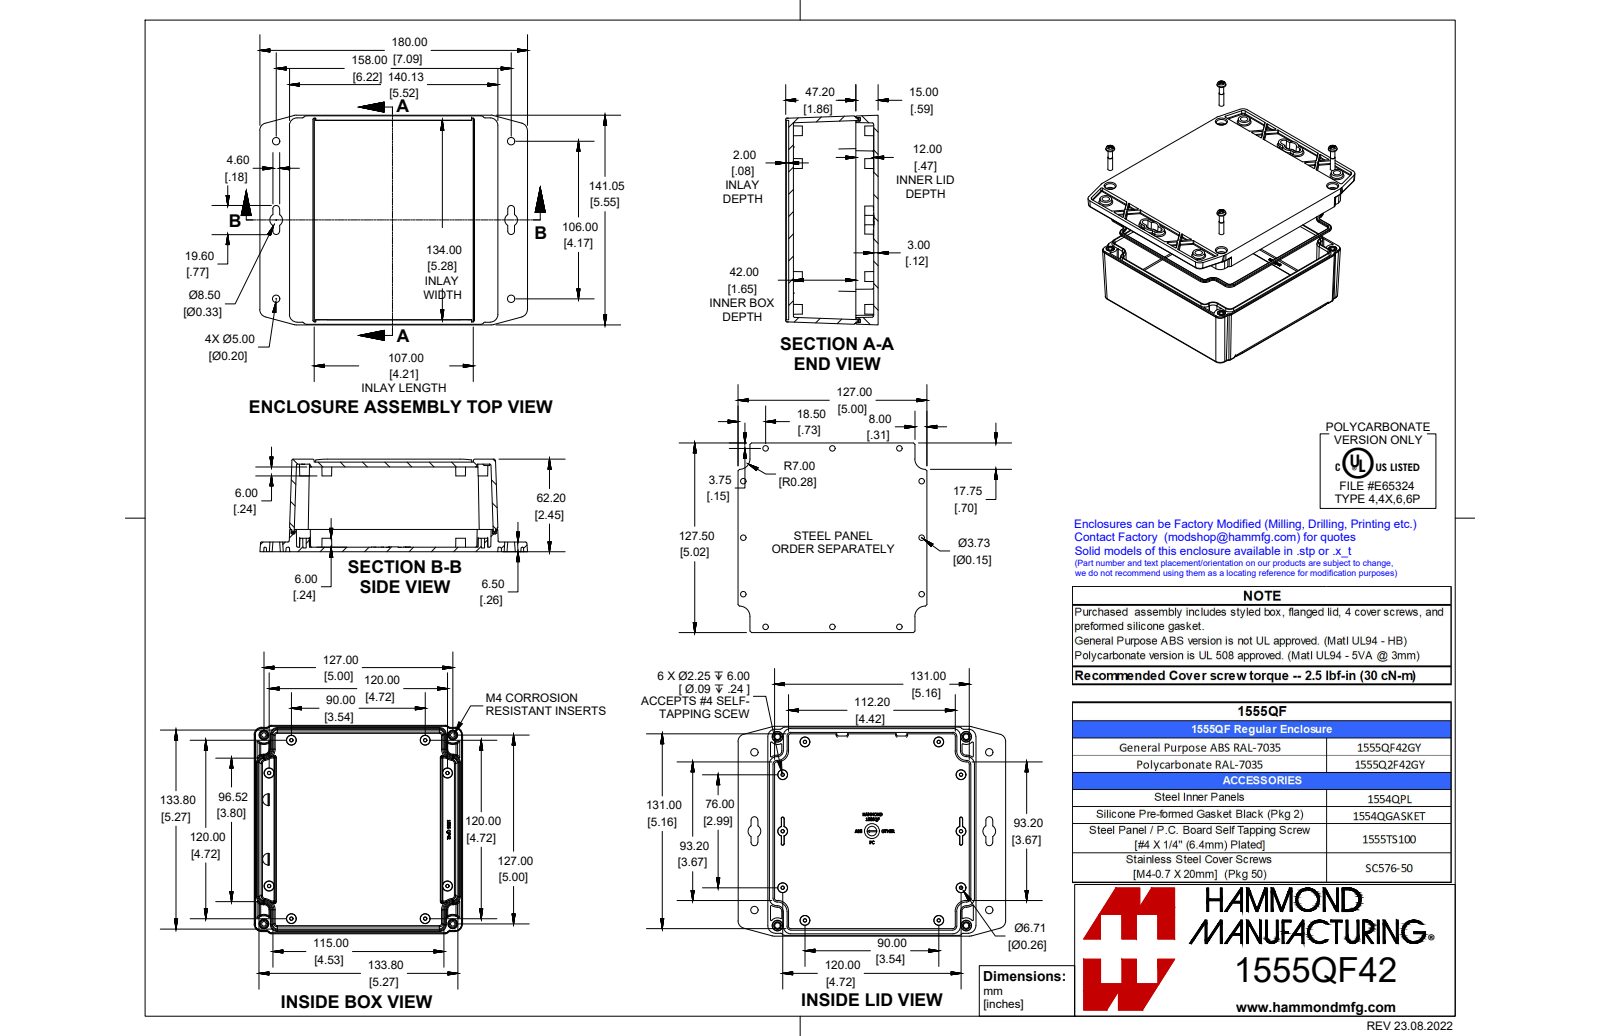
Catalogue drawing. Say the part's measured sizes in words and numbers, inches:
The part is named "1555Q2F42GY". Its 3-D file was written by "SolidWorks 2021 (AUTOMOTIVE_DESIGN)". It is 7 solids with 1342 faces: 444 planar, 324 cylindrical and 574 other. Overall it measures 7.087 by 5.553 by 2.449 inches. Its volume is 16.25 cubic inches and its surface area 274.2 square inches. Round holes: 4 of diameter 0.128, 4 of diameter 0.158. Round bosses or shafts: 4 of diameter 0.276, 4 of diameter 0.153, 4 of diameter 0.138. Partial cylindrical surfaces (rounded edges, fillets, slot ends): 118 of radius 0.02, 49 of radius 0.031, 16 of radius 0.012, 8 of radius 0.039, 8 of radius 0.104, 8 of radius 0.197, 8 of radius 0.199, 4 of radius 0.118. The main face-to-face distances are 0.126, 0.118, 2.252, 2.37, 2.126, 2.244, 0.122, 0.138, 0.256, 2.114. The hole center spacings are 5, 7.071.
